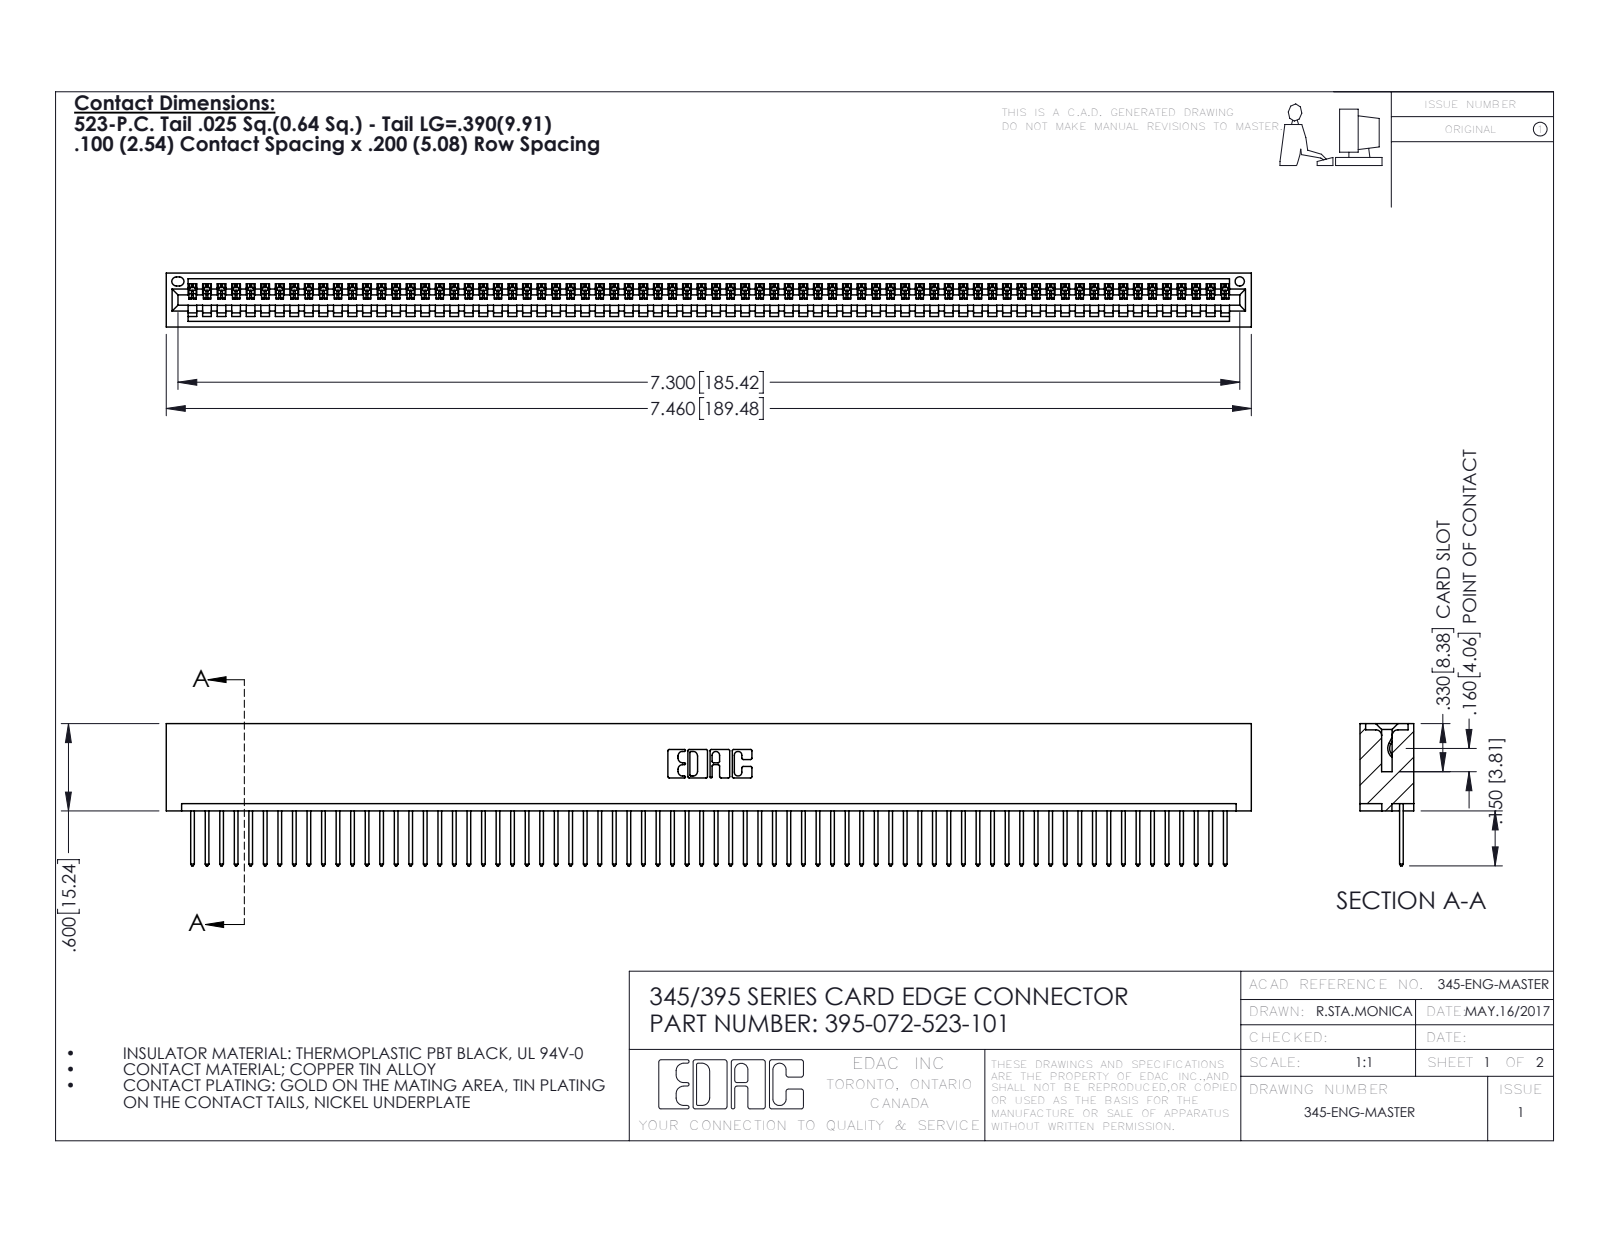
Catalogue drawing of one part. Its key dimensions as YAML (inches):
part_name: "345 Part_No Mounting Lugs; 345-292-001_345-293-123; 395-072-523-101"
step_written_by: "SolidWorks 2016 (CONFIG_CONTROL_DESIGN)"
units: inches
bodies: {solids: 73, faces: 4294, planar: 2956, cylindrical: 1338, other: 0}
overall_size: [7.46, 0.977, 0.37]
volume: 1.147
surface_area: 39.77
round_holes:
  - {diameter: 0.064, count: 1}
partial_cylinders:
  - {radius: 0.006, count: 144}
  - {radius: 0.01, count: 144}
  - {radius: 0.01, count: 22}
  - {radius: 0.007, count: 6}
  - {radius: 0.031, count: 6}
  - {radius: 0.026, count: 3}
  - {radius: 0.031, count: 2}
  - {radius: 0.04, count: 2}
face_to_face_distances: [0.298, 0.072, 0.37, 0.2, 0.098, 0.272, 0.025, 0.225, 0.149, 0.072]
